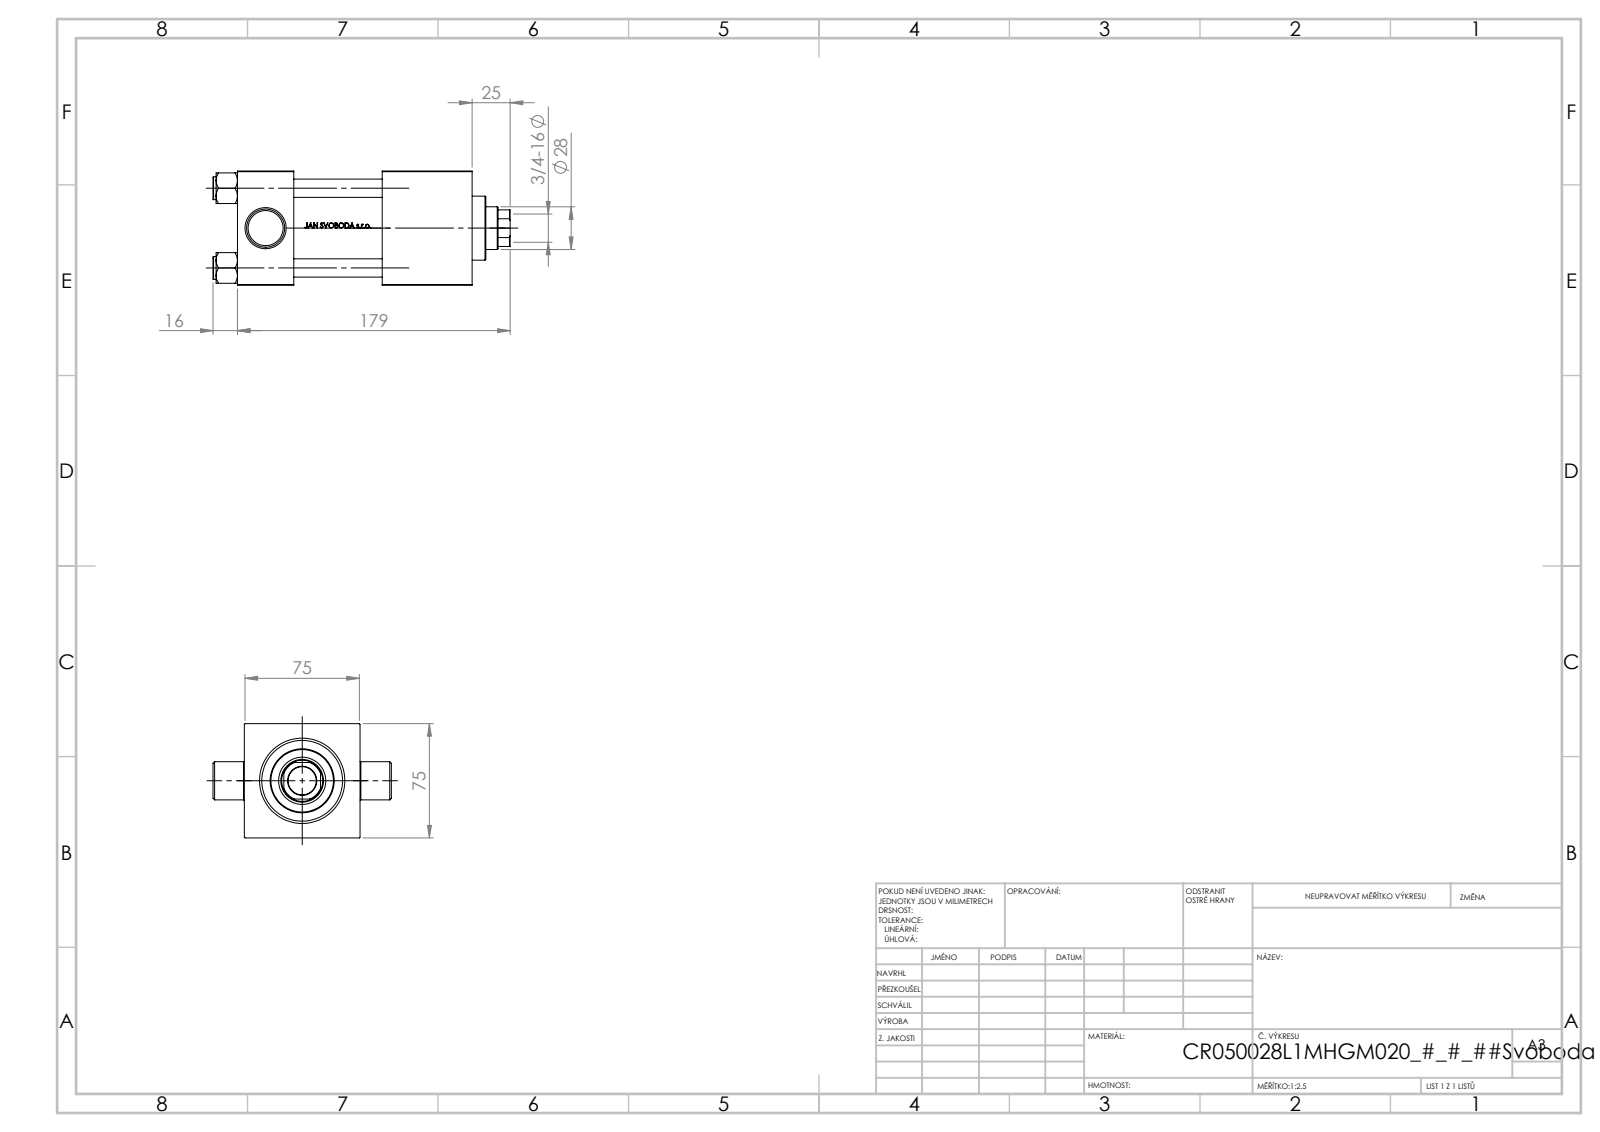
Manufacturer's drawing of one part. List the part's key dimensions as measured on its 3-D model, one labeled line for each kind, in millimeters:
Part name (STEP PRODUCT): NUT_M5_L; V215CR_VCP_L; V215CR_L_TYCINKA; V215CR_L_Body (+1 more)
STEP written by: SolidWorks 2019 (CONFIG_CONTROL_DESIGN)
Units: millimetres
Bodies: 11 solids, 1057 faces (425 planar, 110 cylindrical, 522 other)
Overall size (bounding box): 195 × 117 × 75
Volume: 713 380 mm³ · Surface area: 147 547 mm²
Round holes (diameter × count): ⌀12 ×4, ⌀7 ×1, ⌀18.5 ×1, ⌀28 ×1, ⌀31 ×1, ⌀41 ×1, ⌀50 ×1, ⌀53 ×1
Round bosses / shafts (diameter × count): ⌀15 ×4, ⌀56 ×1, ⌀42 ×1, ⌀25 ×1
Partial cylindrical surfaces — rounded edges, fillets, slot ends (radius × count): R13.5 ×1
Main face-to-face distances: 75, 37, 117, 0.5, 76, 75.5, 154, 58, 59, 95
Hole centre spacings: 36.98, 52.3, 73.96
